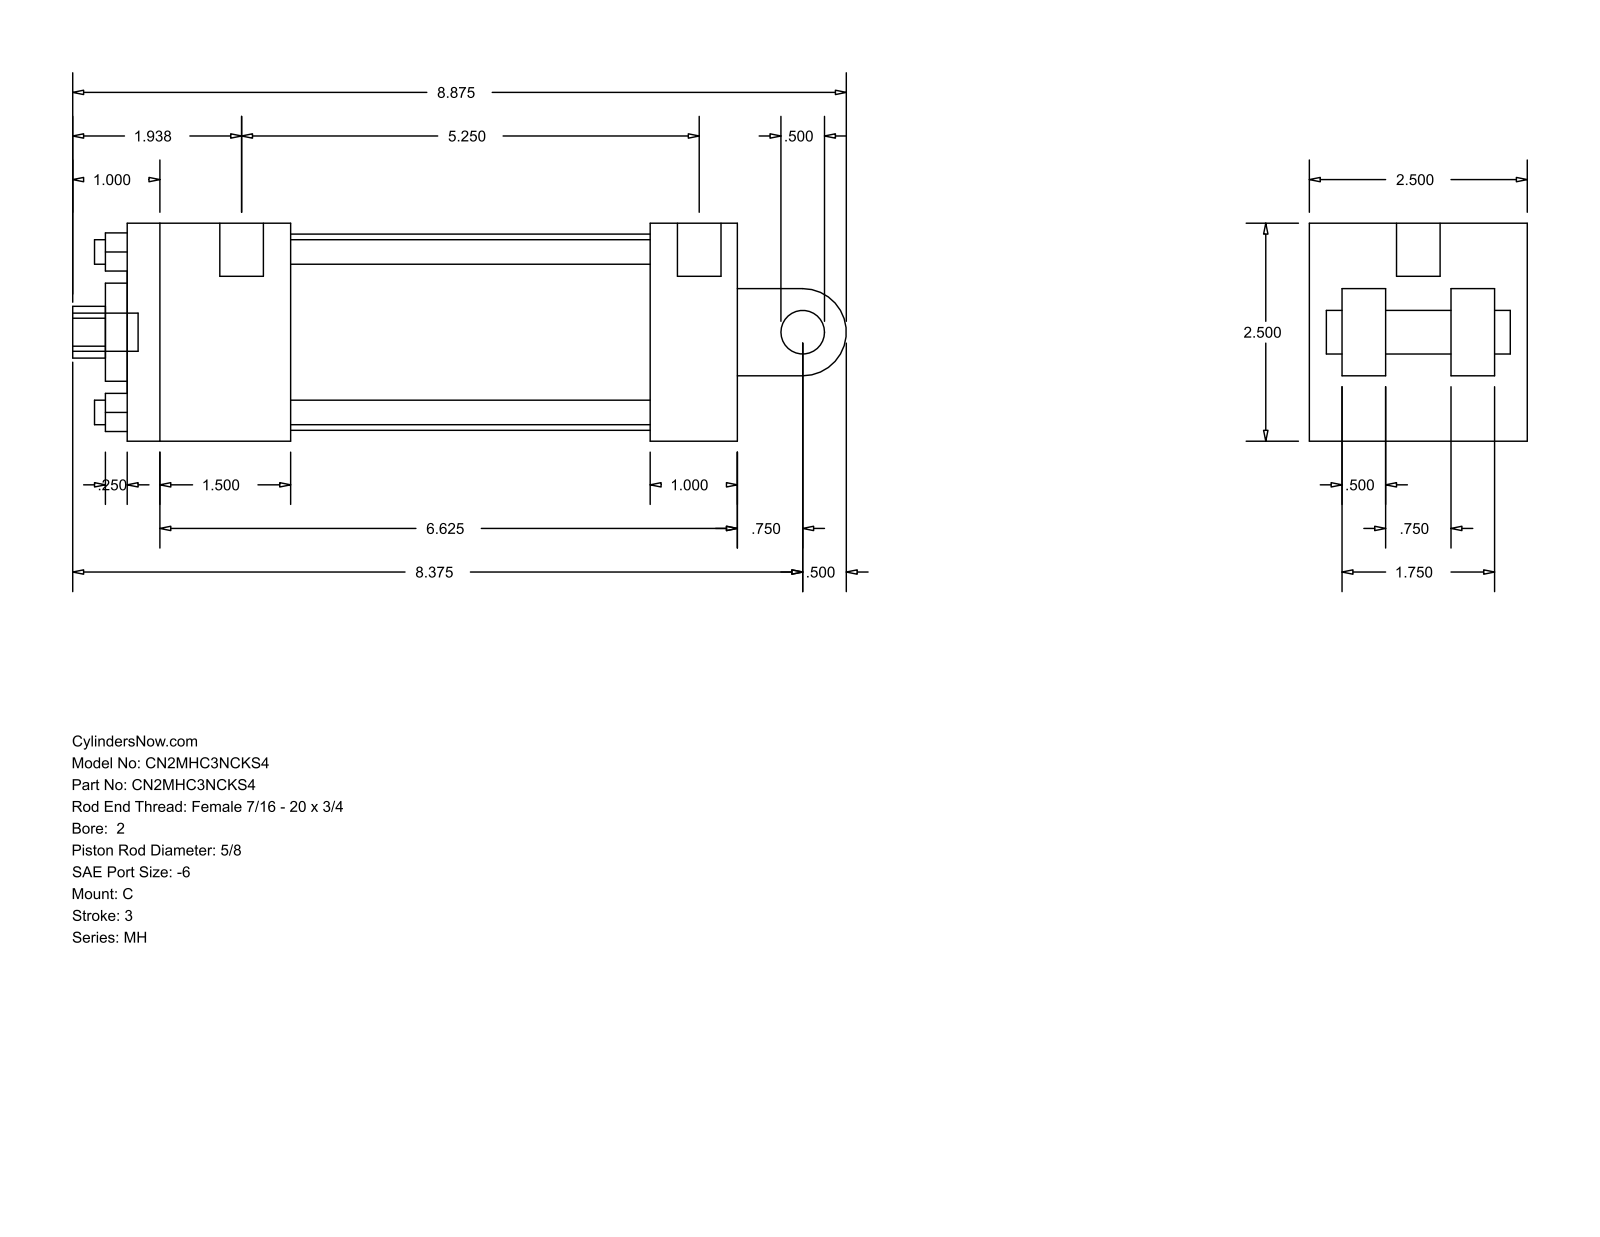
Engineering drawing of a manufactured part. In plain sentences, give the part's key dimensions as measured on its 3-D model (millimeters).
The part is named "MH_C__0200_0.625". Its 3-D file was written by "GSSL Pune (CONFIG_CONTROL_DESIGN)". It is 0 solids with 99 faces: 70 planar, 29 cylindrical and 0 other. Overall it measures 225.43 by 63.5 by 63.5 millimeters. Round holes: 4 of diameter 7.14, 2 of diameter 5.56, 1 of diameter 12.7, 1 of diameter 15.88, 1 of diameter 28.57, 1 of diameter 57.15. Round bosses or shafts: 2 of diameter 12.7, 2 of diameter 5.56, 1 of diameter 11.11. Partial cylindrical surfaces (rounded edges, fillets, slot ends): 1 of radius 7.54, 1 of radius 12.7. The main face-to-face distances are 63.5, 177.8, 25.4, 12.7, 9.52, 47.62, 152.4, 104.78, 130.18, 19.05. The hole center spacings are 33.05, 46.74, 66.1, 3.18.
